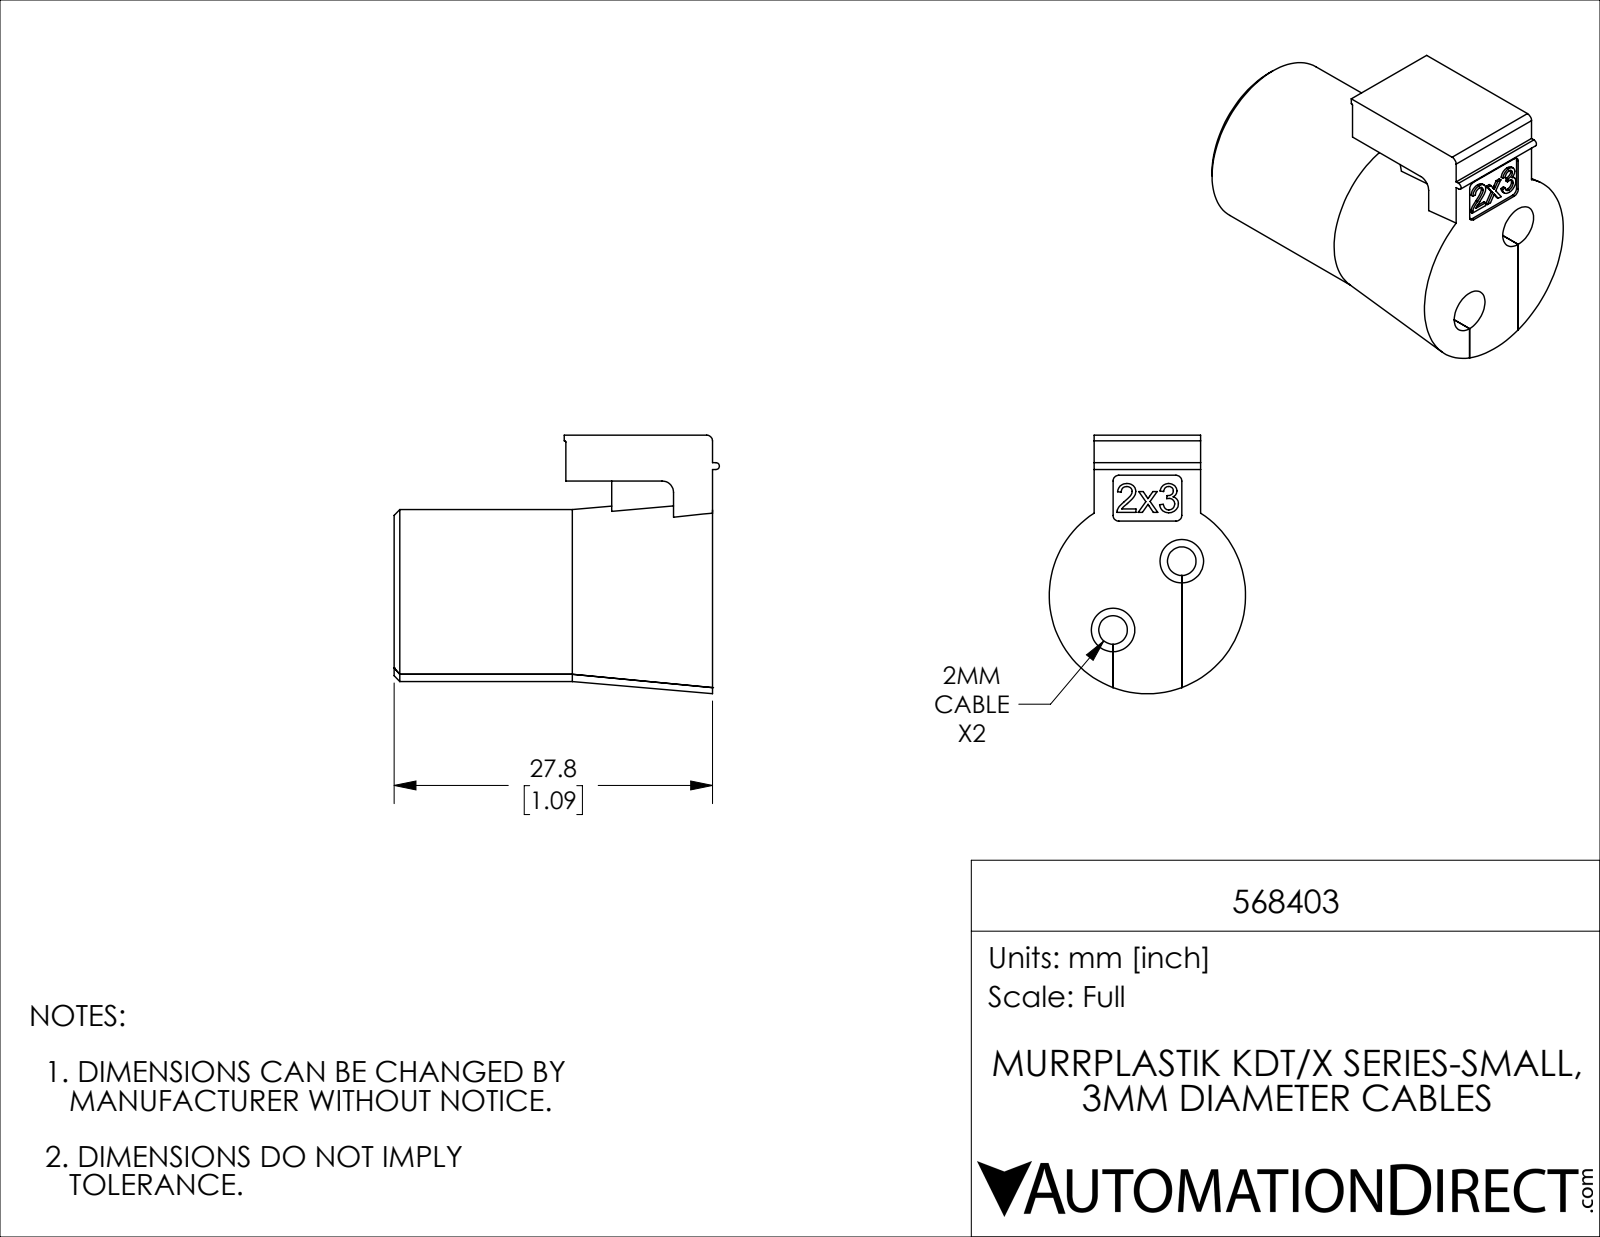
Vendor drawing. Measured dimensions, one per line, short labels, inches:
name: 568403
written by: SolidWorks 2019 (CONFIG_CONTROL_DESIGN)
unit: in
bodies: 1 solid, 118 faces (49 planar, 28 cylindrical, 41 other)
size: 1.118 × 0.889 × 0.675
volume: 0.318 in³; area: 5.19 in²
holes: 2× ⌀0.098, 2× ⌀0.15
bosses: 1× ⌀0.591
rounds: 5× R0.02, 1× R0.004, 1× R0.012, 1× R0.039
face distances: 1.094, 0.236, 0.065, 0.301, 0.157, 0.237, 0.236, 0.302, 0.065, 0.065
hole spacings: 0.334
